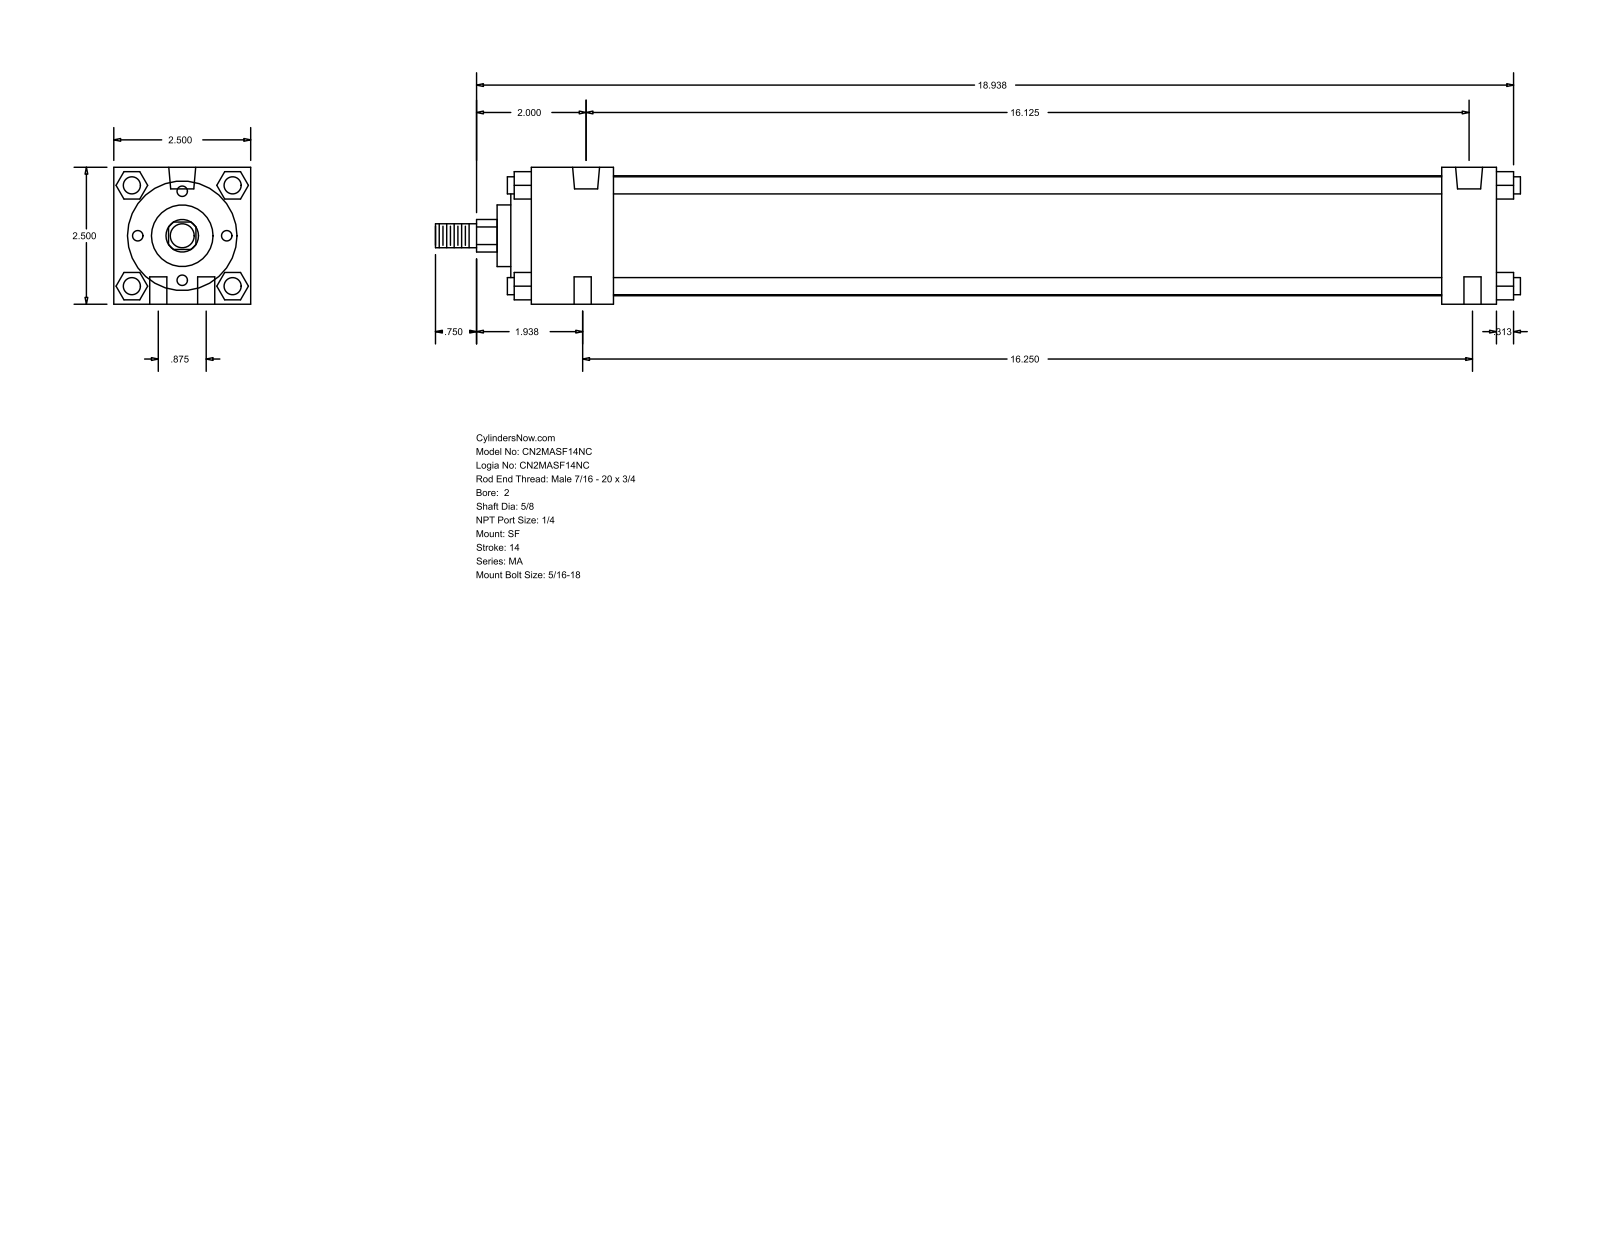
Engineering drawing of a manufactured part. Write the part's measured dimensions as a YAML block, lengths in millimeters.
part_name: "MA_SF__0200_0.625"
step_written_by: "GSSL Pune (CONFIG_CONTROL_DESIGN)"
units: millimeters
bodies: {solids: 0, faces: 126, planar: 95, cylindrical: 31, other: 0}
overall_size: [503.24, 63.5, 63.5]
round_holes:
  - {diameter: 7.94, count: 6}
  - {diameter: 12.49, count: 2}
round_bosses_or_shafts:
  - {diameter: 7.94, count: 4}
  - {diameter: 55.63, count: 1}
  - {diameter: 50.8, count: 1}
  - {diameter: 28.57, count: 1}
  - {diameter: 15.88, count: 1}
  - {diameter: 11.11, count: 1}
partial_cylinders:
  - {radius: 7.54, count: 1}
face_to_face_distances: [63.5, 12.7, 38.1, 447.67, 422.28, 25.39, 384.18, 409.57, 9.52, 47.62]
hole_center_spacings: [11.22, 22.22, 409.58, 411.31, 411.32, 412.75, 413.35]
